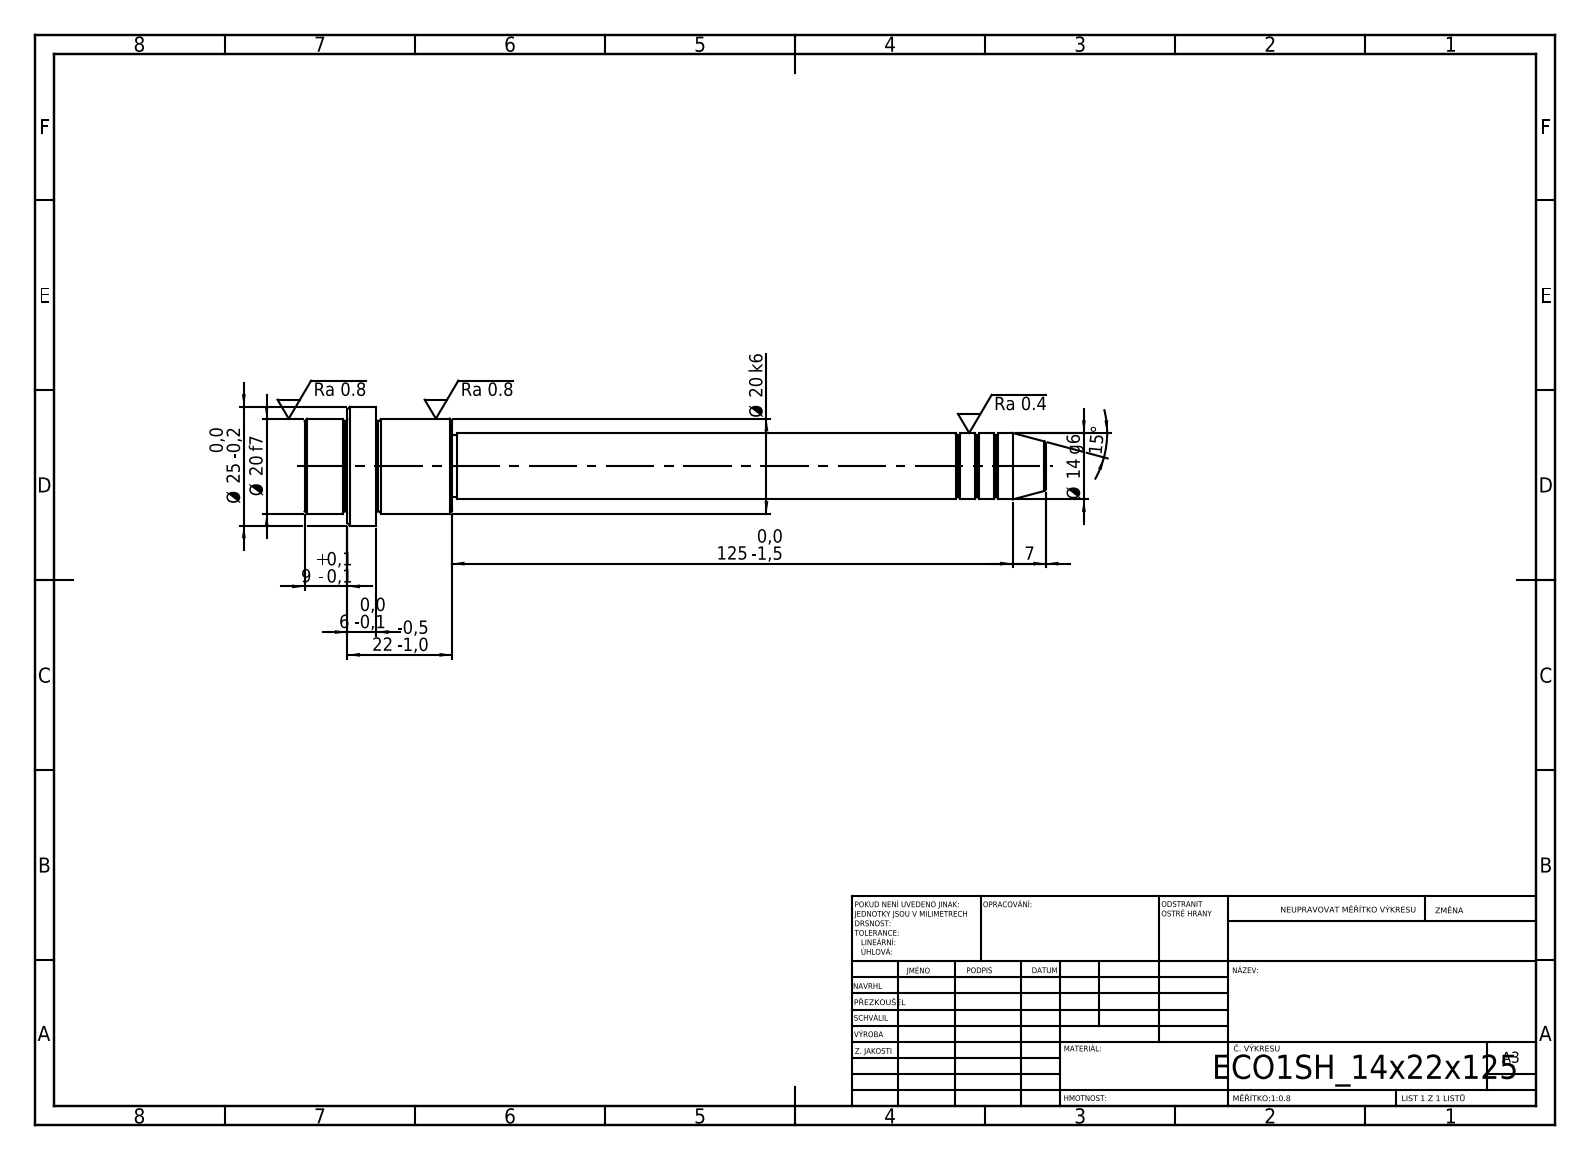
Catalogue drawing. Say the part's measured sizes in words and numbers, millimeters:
Its 3-D file was written by "SolidWorks 2019 (CONFIG_CONTROL_DESIGN)". It is 1 solid with 52 faces: 6 planar, 16 cylindrical and 30 other. Overall it measures 156 by 25 by 25 millimeters. Its volume is 29 633 cubic millimeters and its surface area 8 524 square millimeters. Round bosses or shafts: 1 of diameter 25, 1 of diameter 20, 1 of diameter 14, 1 of diameter 13. The main face-to-face distances are 15, 16, 31, 22, 6, 9, 125, 141, 147, 156.
